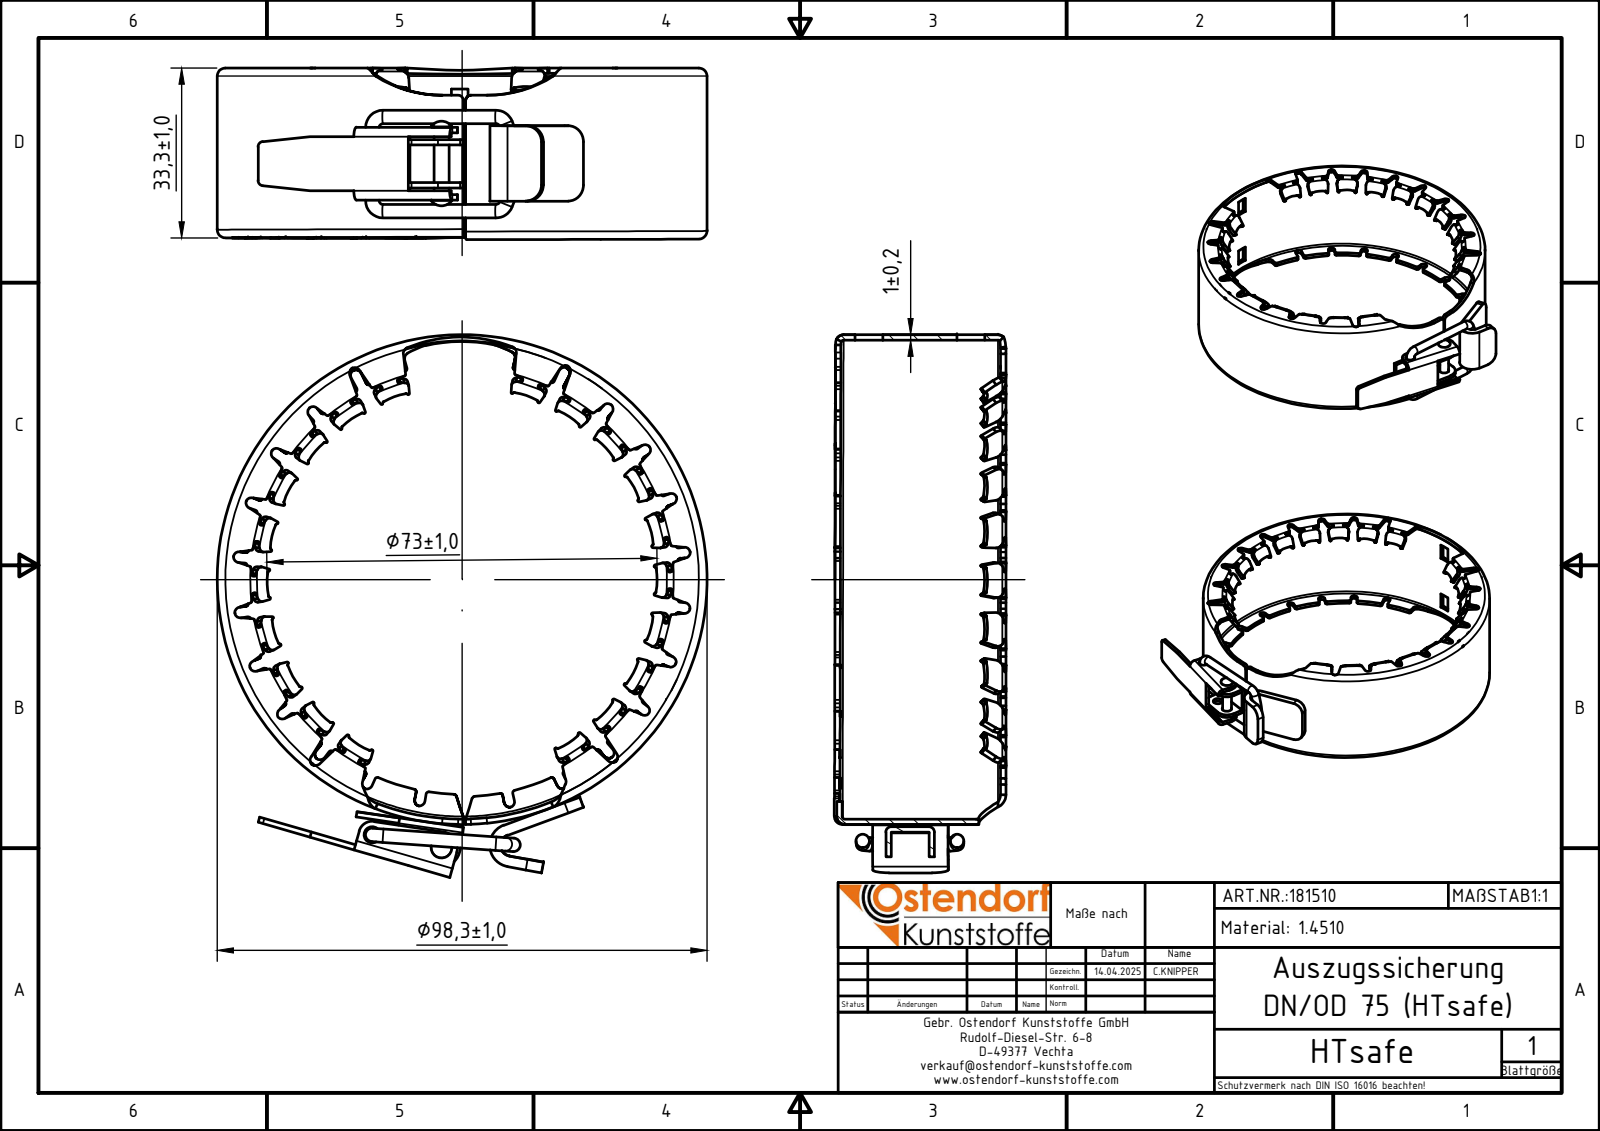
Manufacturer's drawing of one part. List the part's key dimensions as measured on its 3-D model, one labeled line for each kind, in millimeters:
Part name (STEP PRODUCT): 881510z
STEP written by: Autodesk Inventor 2024 (AUTOMOTIVE_DESIGN)
Units: millimetres
Bodies: 6 solids, 1224 faces (74 planar, 57 cylindrical, 1093 other)
Overall size (bounding box): 100.75 × 90.93 × 31.85
Volume: 12 978 mm³ · Surface area: 26 555 mm²
Round holes (diameter × count): ⌀3 ×3
Round bosses / shafts (diameter × count): ⌀2.5 ×3, ⌀2.8 ×1
Partial cylindrical surfaces — rounded edges, fillets, slot ends (radius × count): R1.92 ×14, R1.92 ×5, R3 ×5, R1 ×4, R0.74 ×2, R1.74 ×2, R3.5 ×2, R1.92 ×1
Main face-to-face distances: 1, 2, 23.5, 11.03, 12.47, 8, 0.99, 13.28, 10.22, 2.25
Hole centre spacings: 5.01, 8.05, 13.06
